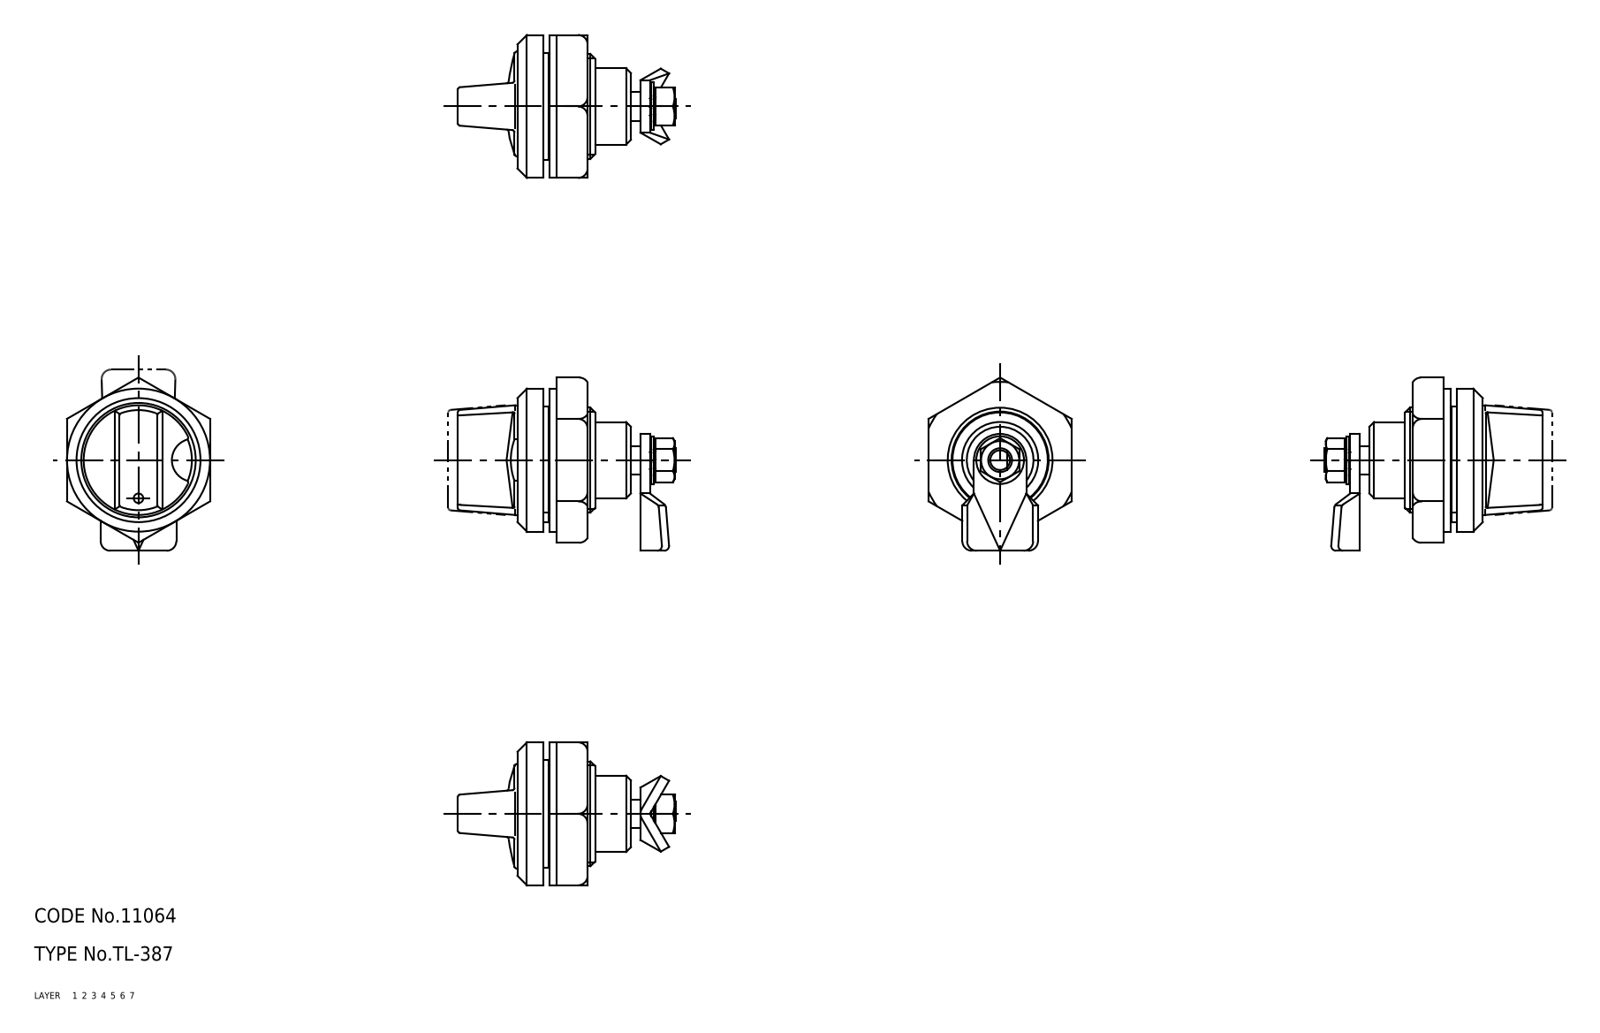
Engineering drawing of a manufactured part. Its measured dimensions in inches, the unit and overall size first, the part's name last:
Units: inches
Overall size (bounding box): 1.803 × 1.43 × 1.181
Volume: 0.313 in³ · Surface area: 11.94 in²
Bodies: 2 solids, 141 faces (0 planar, 0 cylindrical, 141 other)
Part name (STEP PRODUCT): 67118745; 67118758; 67118771; 67118784 (+8 more)
STEP written by: CADfix (AUTOMOTIVE_DESIGN)
